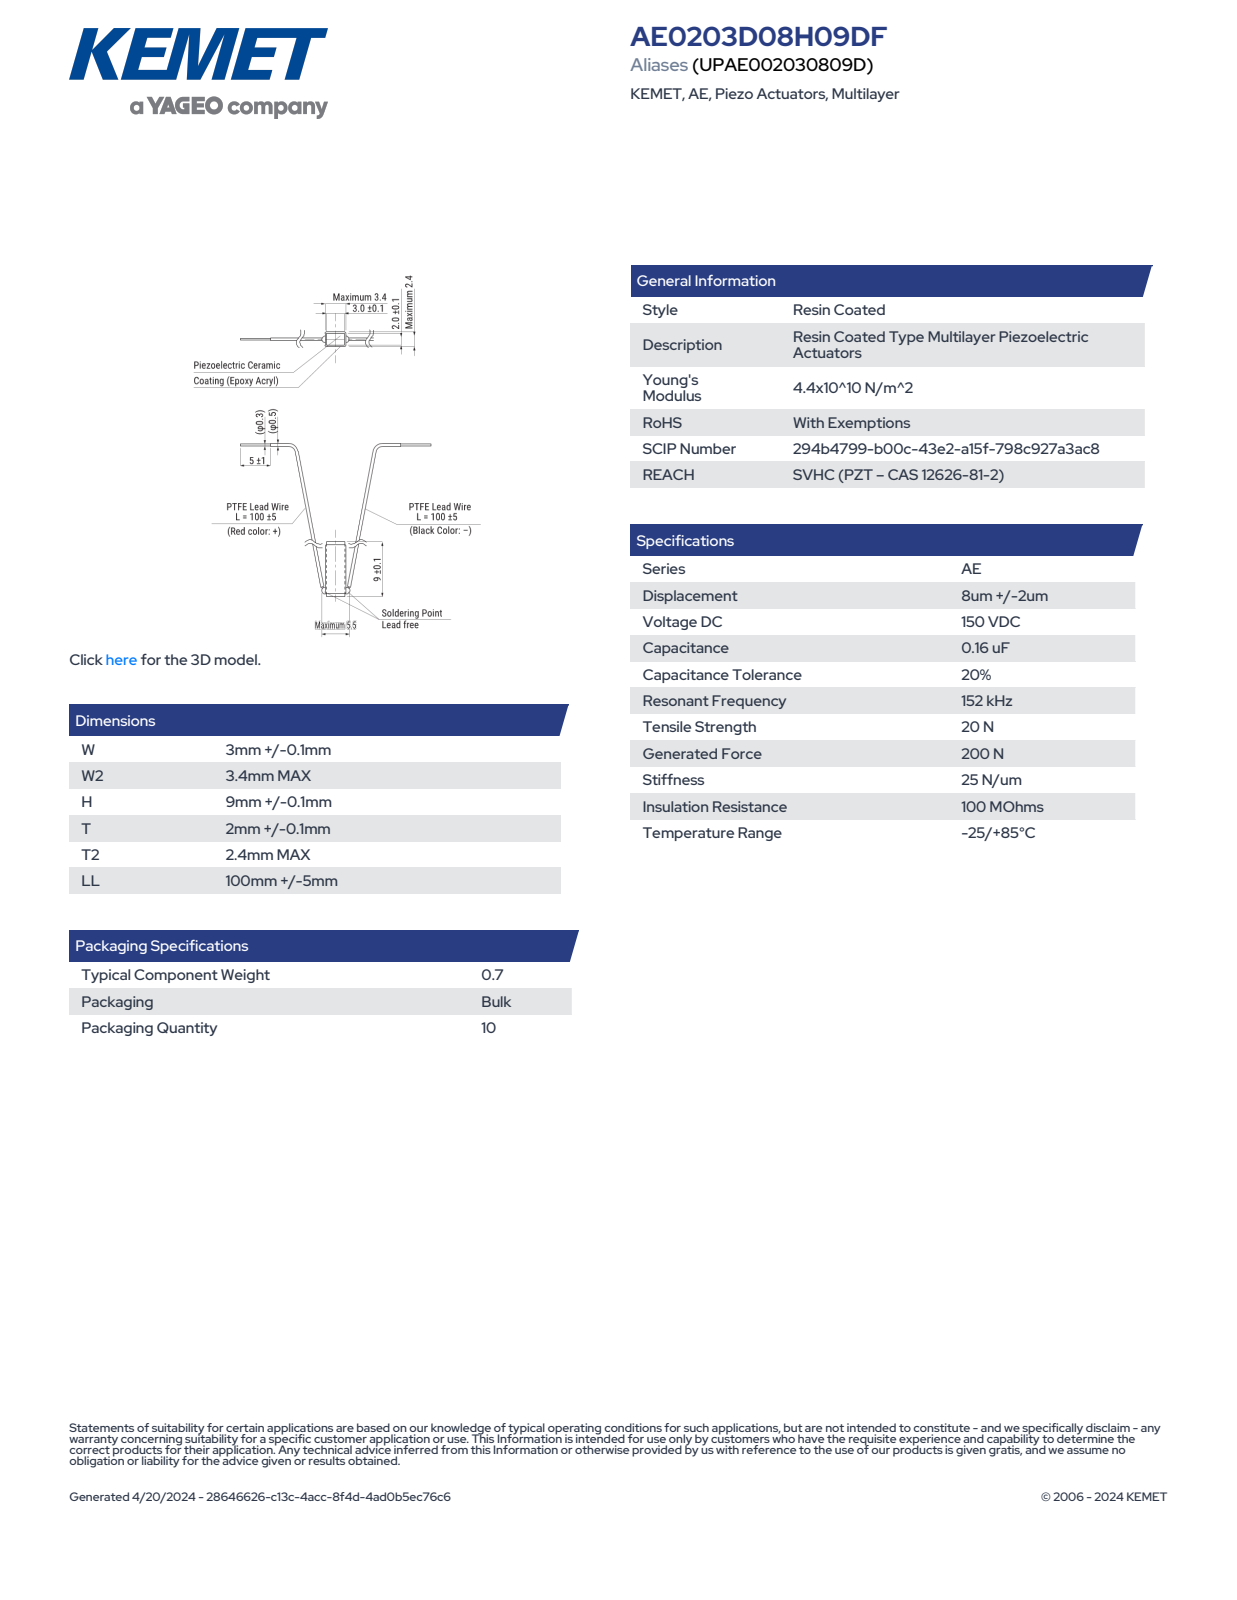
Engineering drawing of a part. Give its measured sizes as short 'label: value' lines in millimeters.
name: AL_KAE1_W3.1W23.4H9.1T2.1T22.4
written by: SolidWorks 2014 (AUTOMOTIVE_DESIGN)
unit: mm
bodies: 4 solids, 93 faces (85 planar, 8 cylindrical, 0 other)
size: 9.11 × 3.4 × 2.4
volume: 60 mm³; area: 116 mm²
rounds: 8× R0.15
face distances: 2.25, 3, 2.1, 2.9, 2.4, 3.1, 9.1, 0.89, 3.66, 5.44
